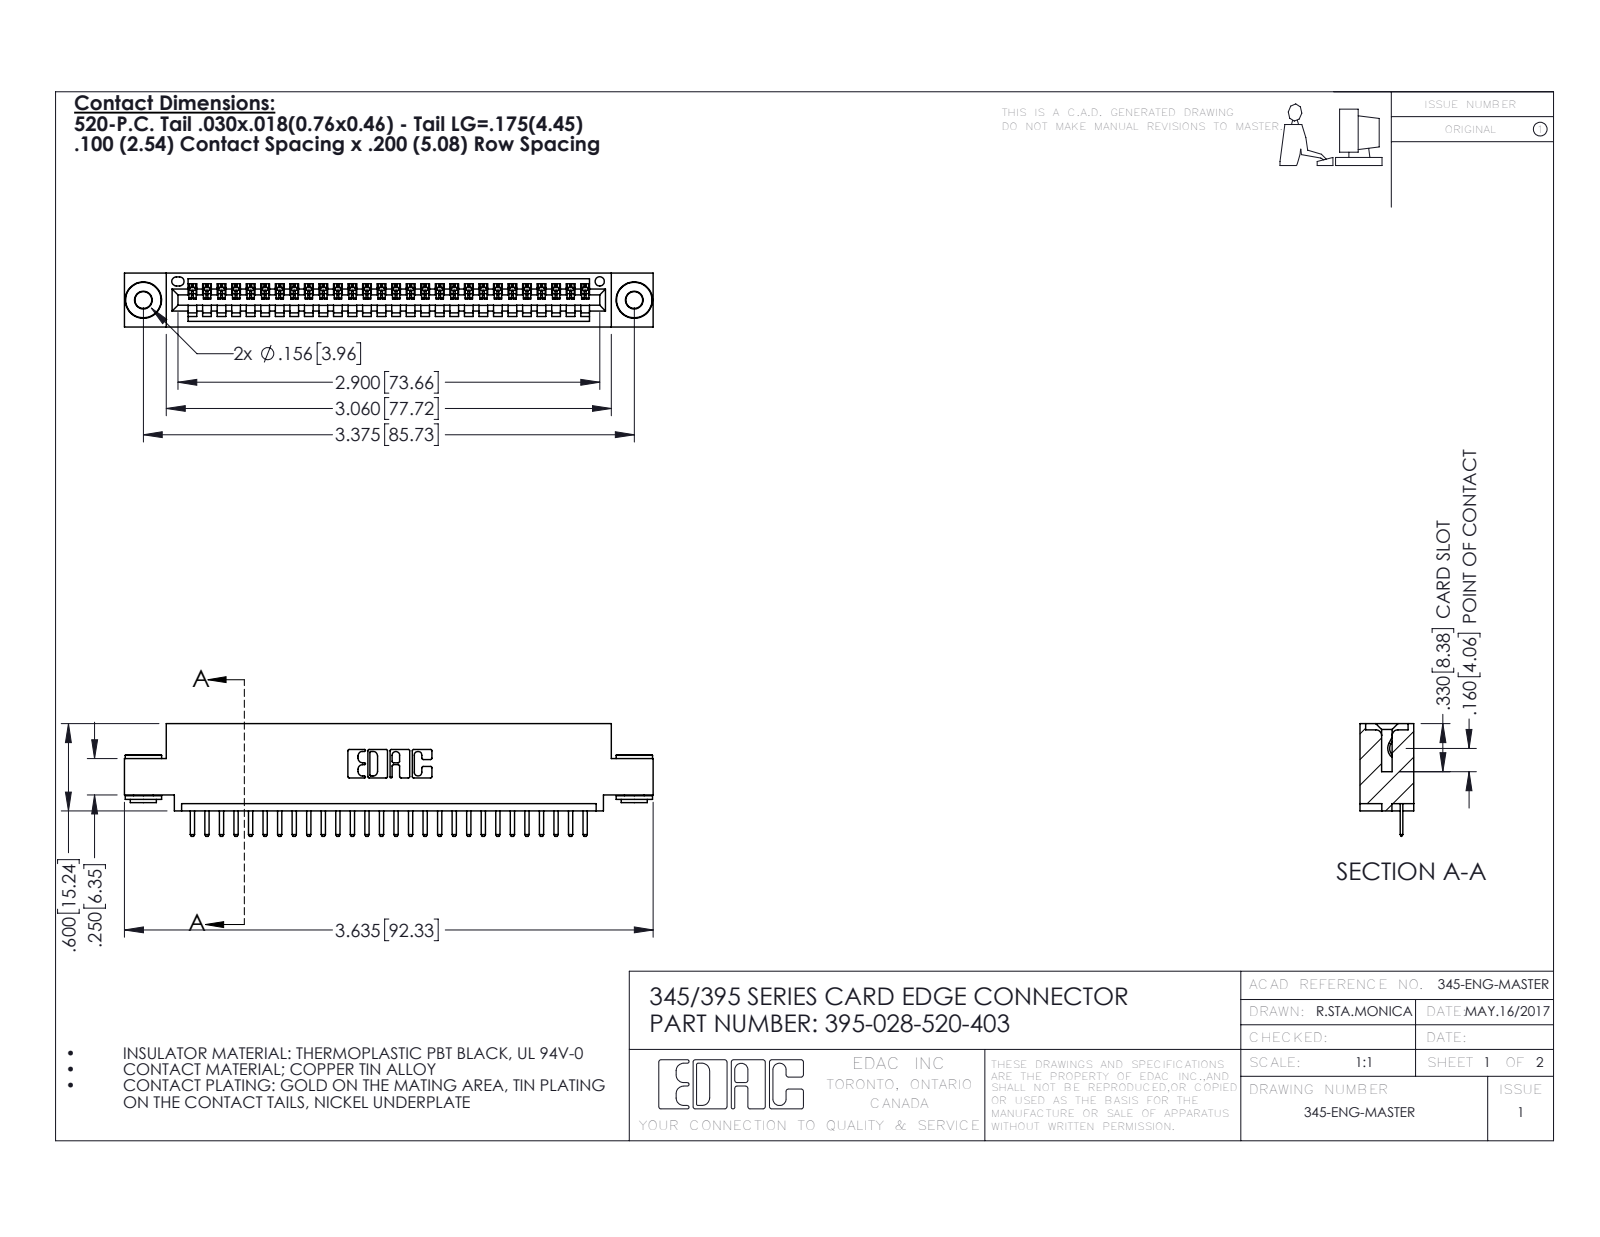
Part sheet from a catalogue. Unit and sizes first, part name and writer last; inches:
Units: inches
Overall size (bounding box): 3.635 × 0.775 × 0.37
Round holes (diameter × count): ⌀0.116 ×2, ⌀0.156 ×2, ⌀0.064 ×1
Round bosses / shafts (diameter × count): ⌀0.25 ×2, ⌀0.18 ×2, ⌀0.136 ×2
Partial cylindrical surfaces — rounded edges, fillets, slot ends (radius × count): R0.01 ×58, R0.006 ×56, R0.01 ×22, R0.007 ×6, R0.031 ×6, R0.026 ×3, R0.031 ×2, R0.04 ×2
Main face-to-face distances: 0.072, 0.298, 0.37, 0.2, 0.025, 0.098, 0.272, 0.225, 0.072, 0.149
Hole centre spacings: 0.27, 3.14, 3.375
Volume: 0.52 in³ · Surface area: 17.31 in²
Bodies: 31 solids, 1904 faces (1270 planar, 626 cylindrical, 8 other)
Part name (STEP PRODUCT): 345 Part_0.110 Offset - 0.156 Dia-TH; 395-028-520-403; 345-250-002_345-250-002-102; 345-292-001_345-293-120
STEP written by: SolidWorks 2016 (CONFIG_CONTROL_DESIGN)
